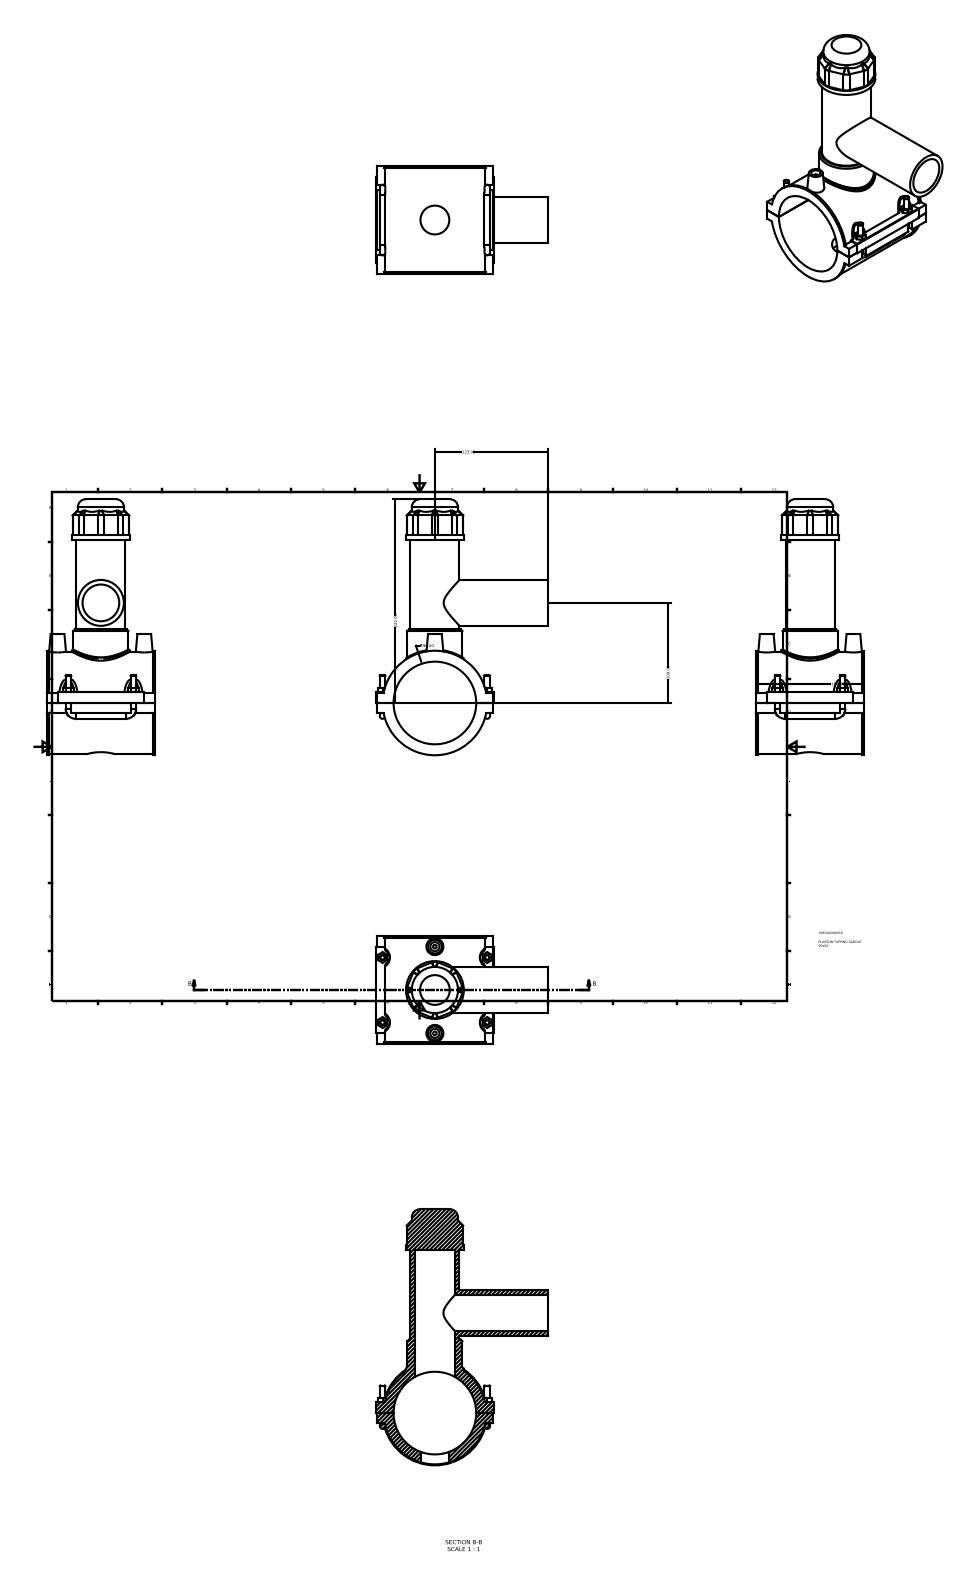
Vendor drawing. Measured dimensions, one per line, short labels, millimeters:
name: 496304090050
written by: Autodesk Inventor 2015 (AUTOMOTIVE_DESIGN)
unit: mm
bodies: 1 solid, 228 faces (126 planar, 57 cylindrical, 45 other)
size: 278.92 × 187 × 118
volume: 716 984 mm³; area: 179 246 mm²
holes: 2× ⌀10, 1× ⌀31.36, 1× ⌀40, 1× ⌀44.1, 1× ⌀90
bosses: 6× ⌀6, 2× ⌀4, 1× ⌀113.83, 1× ⌀111.6, 1× ⌀63, 1× ⌀59.85, 1× ⌀53.55, 1× ⌀50.4
rounds: 8× R9, 4× R3, 4× R7.5, 1× R0.5, 1× R58.03
face distances: 118, 1, 177.8, 177.7, 127, 11.2, 11.3, 189, 23.5, 12.3
hole spacings: 47.2, 94.4
